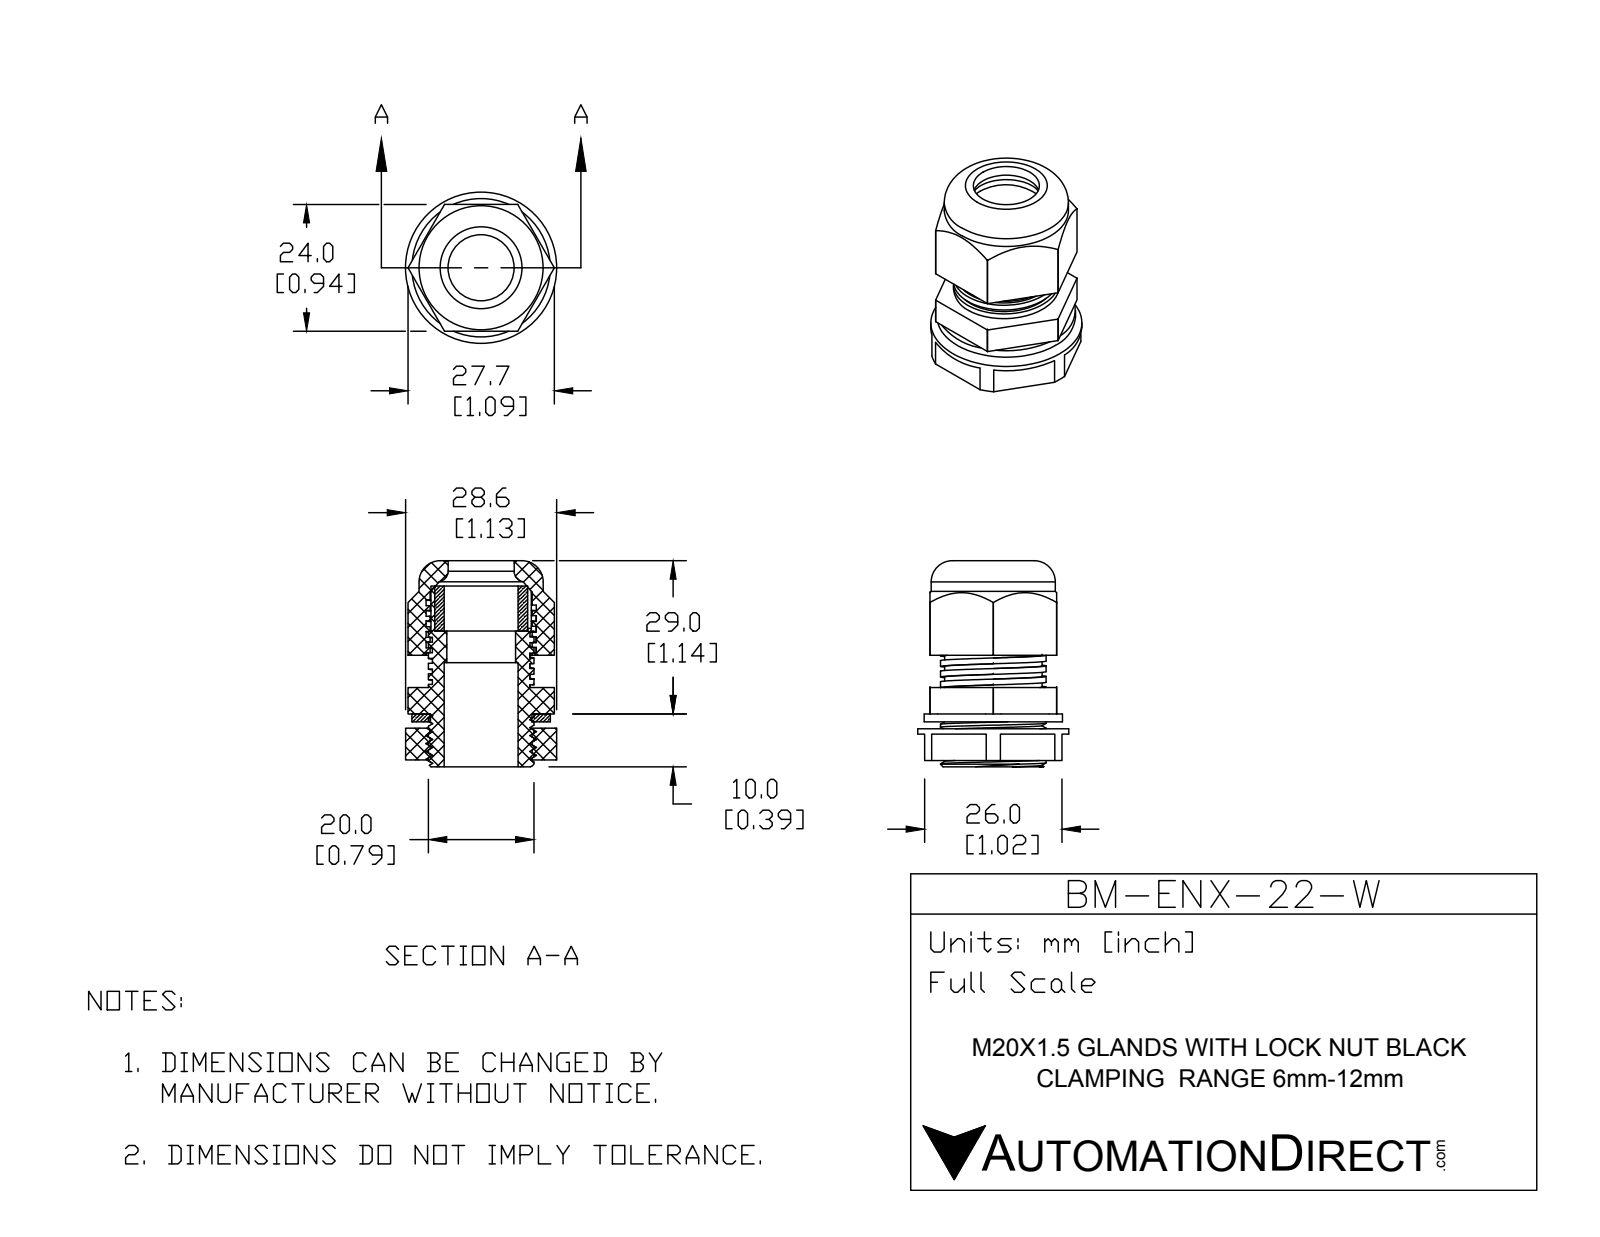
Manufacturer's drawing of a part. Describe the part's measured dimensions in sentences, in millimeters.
The part is named "BM-ENX-22-W". Its 3-D file was written by "SolidWorks 2015 (CONFIG_CONTROL_DESIGN)". It is 5 solids with 246 faces: 140 planar, 84 cylindrical and 22 other. Overall it measures 39 by 28.6 by 28.6 millimeters. Its volume is 11 372 cubic millimeters and its surface area 12 391 square millimeters. Round holes: 1 of diameter 12.5, 1 of diameter 13, 1 of diameter 14, 1 of diameter 17.6, 1 of diameter 19.2, 1 of diameter 19.33. Round bosses or shafts: 1 of diameter 28.6, 1 of diameter 26.2, 1 of diameter 23.5, 1 of diameter 20, 1 of diameter 19. Partial cylindrical surfaces (rounded edges, fillets, slot ends): 1 of radius 13.85. The main face-to-face distances are 24, 1, 8.5, 1.5, 25, 24.2, 7.5, 2.5, 6, 6.5.
